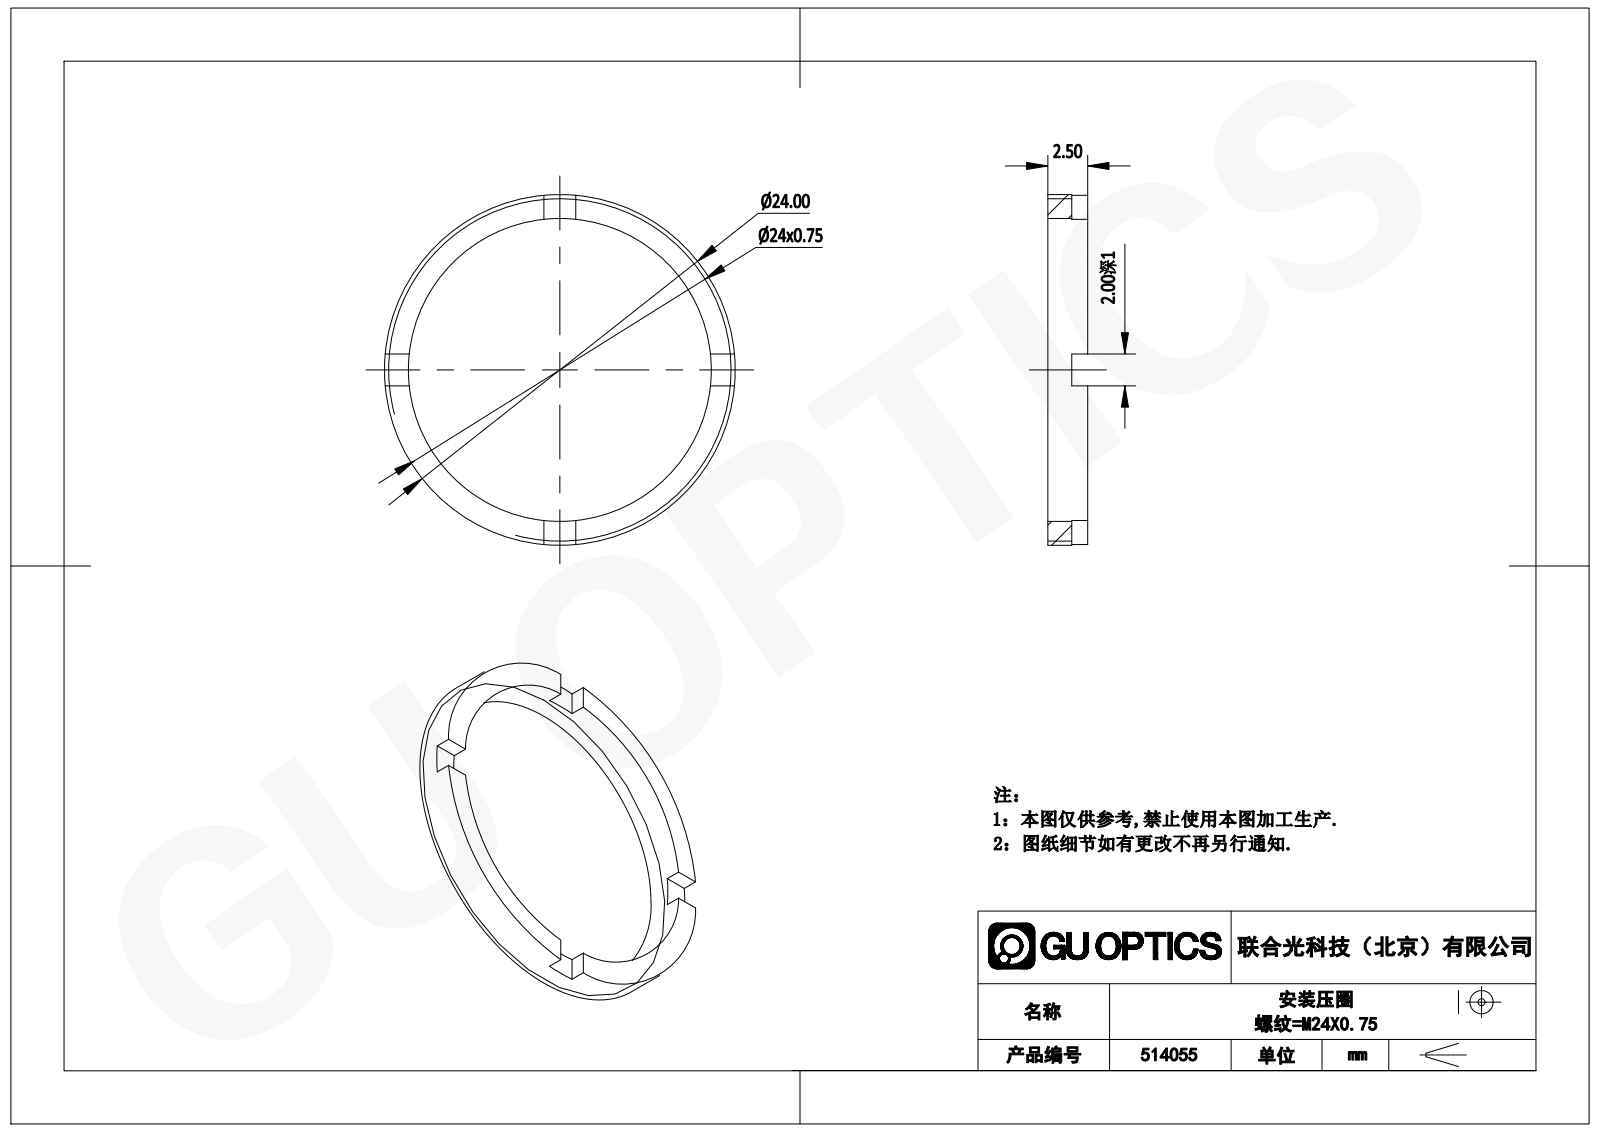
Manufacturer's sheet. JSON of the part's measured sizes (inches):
{"part_name": "514055", "step_written_by": "SolidWorks 2020 (CONFIG_CONTROL_DESIGN)", "units": "inches", "bodies": {"solids": 1, "faces": 21, "planar": 17, "cylindrical": 4, "other": 0}, "overall_size": [0.945, 0.945, 0.098], "volume_in3": 0.015, "surface_area_in2": 0.871, "round_holes": [[0.827, 1]], "round_bosses_or_shafts": [[0.945, 1]], "face_to_face_distances": [0.098, 0.059, 0.039, 0.079]}
